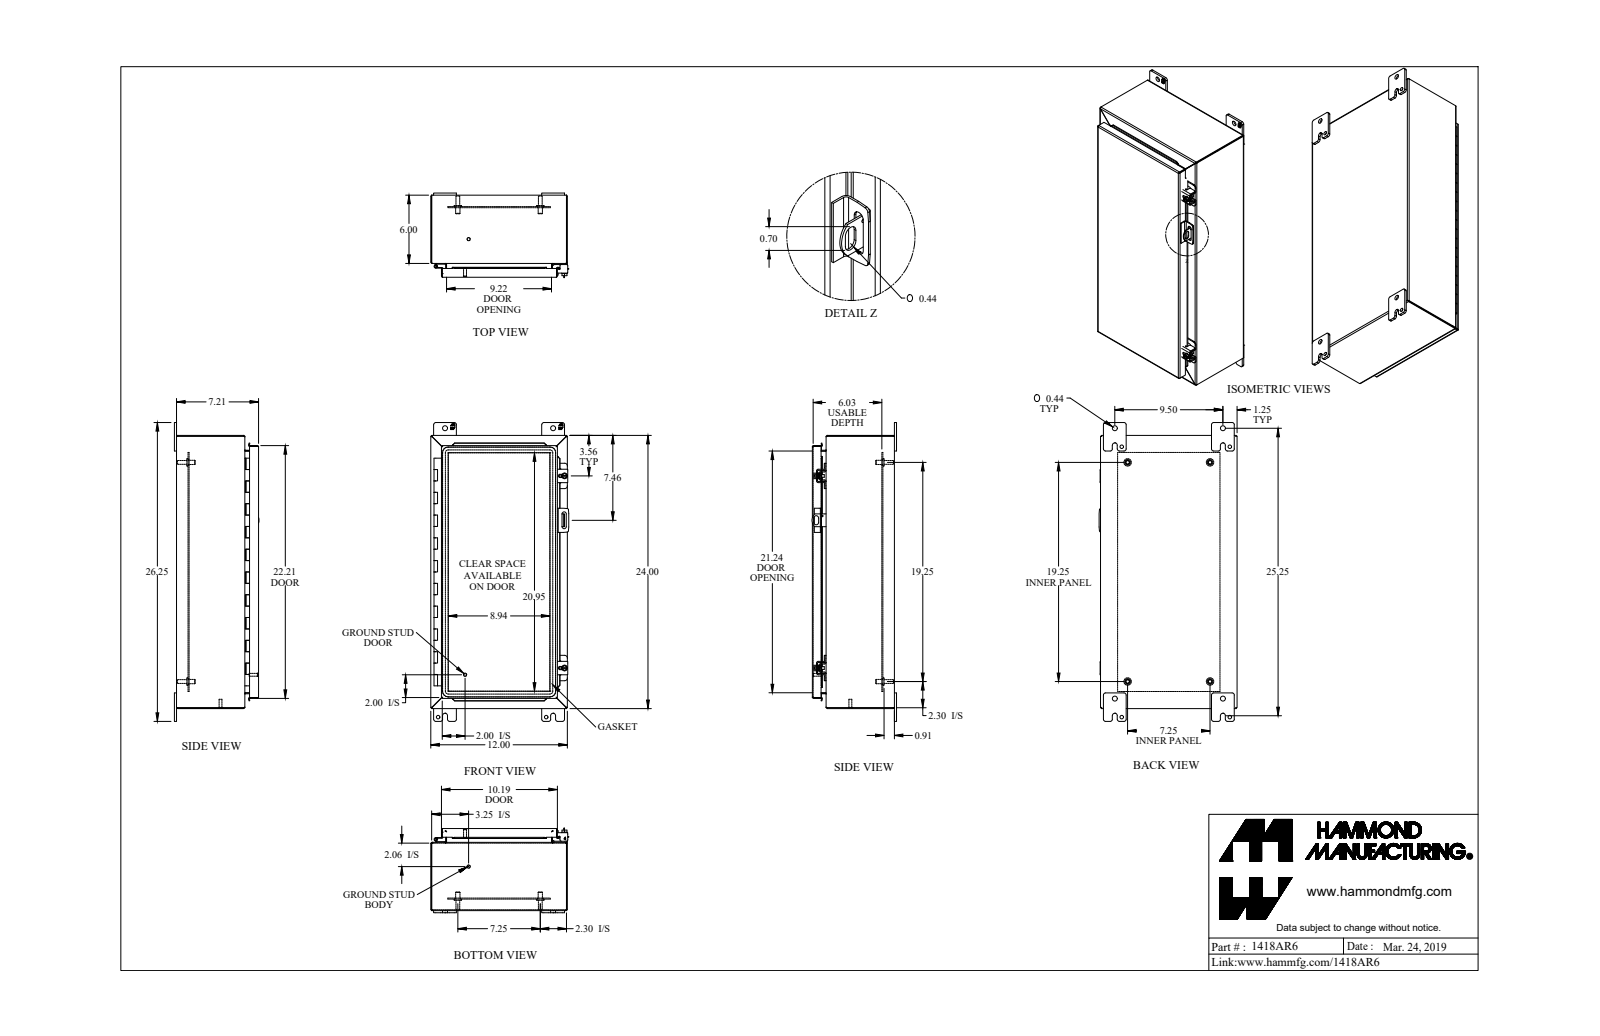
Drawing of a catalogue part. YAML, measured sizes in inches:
part_name: "1418AR6"
step_written_by: "SolidWorks 2019 (AUTOMOTIVE_DESIGN)"
units: inches
bodies: {solids: 38, faces: 1008, planar: 695, cylindrical: 259, other: 54}
overall_size: [26.25, 12.125, 7.437]
volume: 118.6
surface_area: 3081
round_holes:
  - {diameter: 0.313, count: 4}
  - {diameter: 0.437, count: 4}
  - {diameter: 0.5, count: 4}
  - {diameter: 0.213, count: 2}
  - {diameter: 0.265, count: 2}
  - {diameter: 0.307, count: 2}
  - {diameter: 0.375, count: 2}
  - {diameter: 0.445, count: 2}
  - {diameter: 0.125, count: 1}
  - {diameter: 0.187, count: 1}
round_bosses_or_shafts:
  - {diameter: 0.65, count: 4}
  - {diameter: 0.375, count: 4}
  - {diameter: 0.33, count: 4}
  - {diameter: 1, count: 2}
  - {diameter: 0.5, count: 2}
  - {diameter: 0.39, count: 2}
  - {diameter: 0.281, count: 2}
  - {diameter: 0.25, count: 2}
partial_cylinders:
  - {radius: 0.188, count: 26}
  - {radius: 0.036, count: 20}
  - {radius: 0.108, count: 17}
  - {radius: 0.048, count: 13}
  - {radius: 0.143, count: 13}
  - {radius: 0.007, count: 8}
  - {radius: 0.045, count: 8}
  - {radius: 0.079, count: 8}
face_to_face_distances: [0.072, 7.113, 7.041, 11.928, 0.937, 7.185, 1.009, 0.095, 6.081, 6.009]
hole_center_spacings: [20.57, 1.735, 9.5, 19.25, 23.75, 25.58, 2.434, 3.204]
